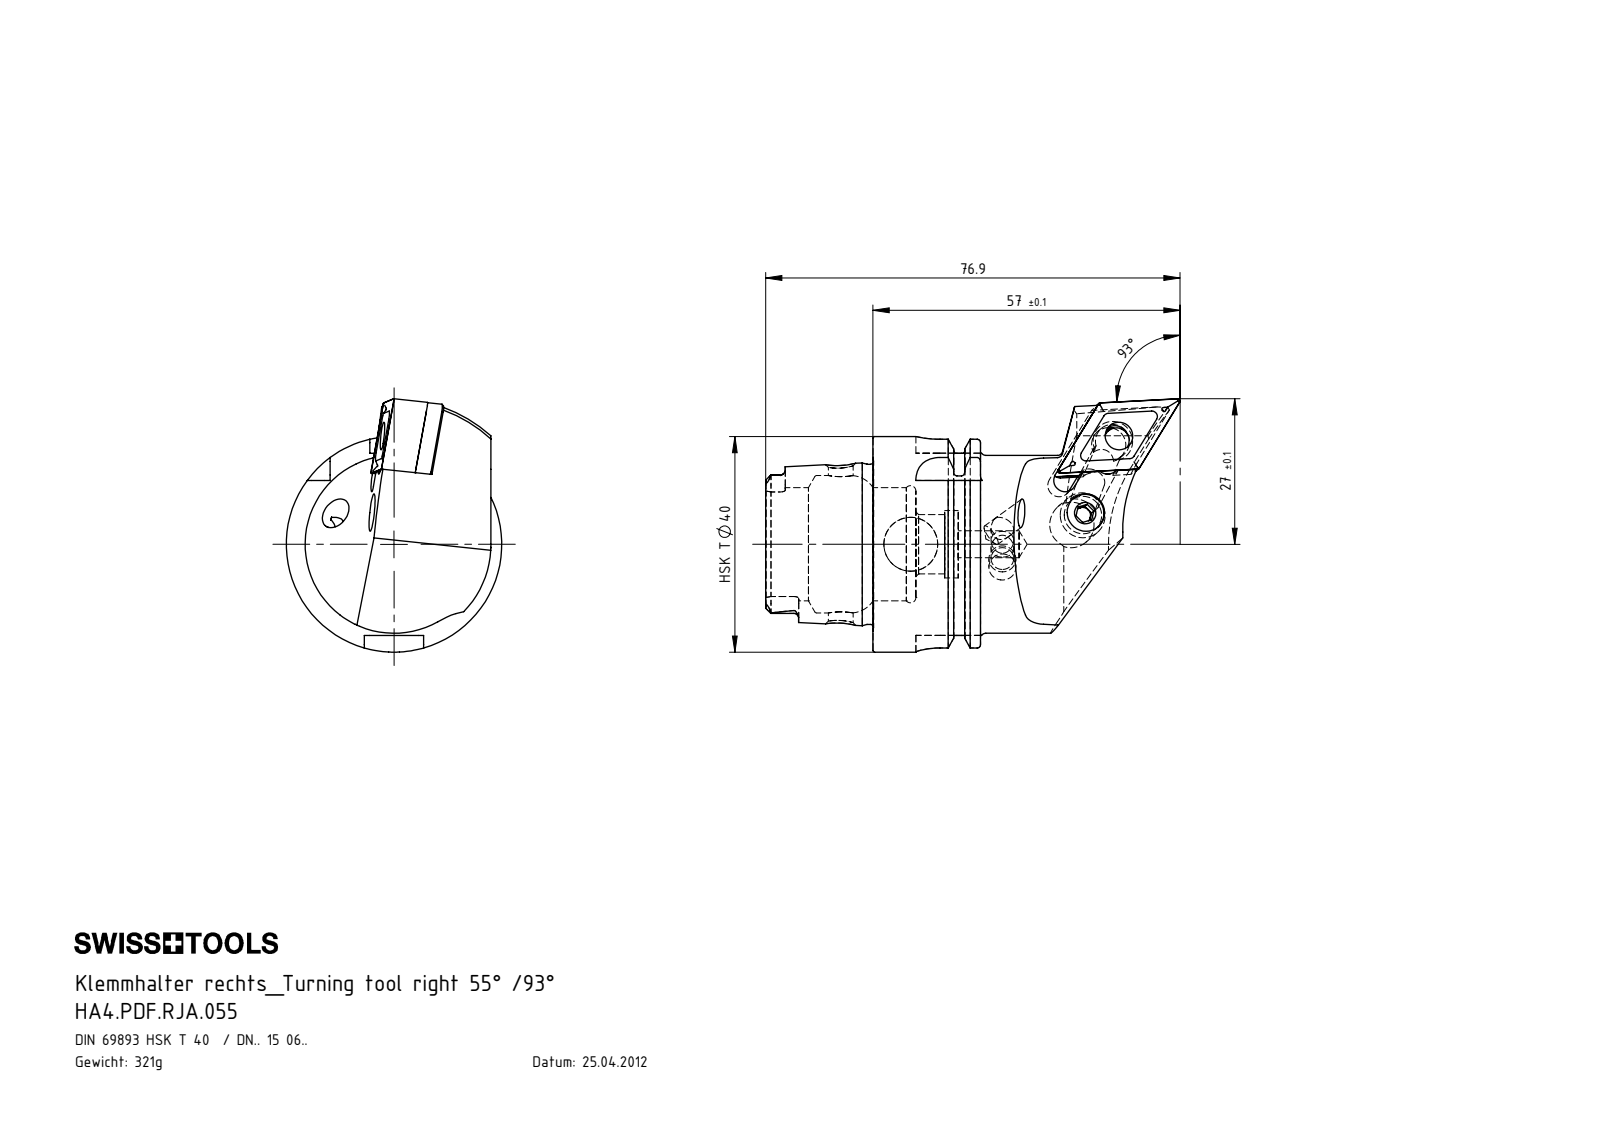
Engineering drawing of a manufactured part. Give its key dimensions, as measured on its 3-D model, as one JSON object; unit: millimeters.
{"part_name": "HA4-PDF.RJA.055; WDF-ER2.101.003_A; WDF-ER3.101.000_A; WCD-ER4.101.017_A (+4 more)", "step_written_by": "SolidWorks 2012 (CONFIG_CONTROL_DESIGN)", "units": "millimeters", "bodies": {"solids": 8, "faces": 385, "planar": 119, "cylindrical": 107, "other": 159}, "overall_size": [76.9, 47, 40], "volume_mm3": 42057, "surface_area_mm2": 16697, "round_holes": [[4.2, 2], [5, 2], [4, 1], [4.6, 1], [5.16, 1], [6.4, 1], [7, 1], [8.4, 1], [10, 1], [11, 1], [12.5, 1], [21, 1]], "round_bosses_or_shafts": [[40, 1], [34.75, 1], [33, 1], [29.71, 1], [8, 1], [7.9, 1], [6.4, 1], [5, 1]], "partial_cylinders_radius": [[0.9, 6], [0.4, 4], [1, 4], [4.5, 4], [1.82, 2], [1.88, 2], [2.5, 2], [2.1, 1]], "face_to_face_distances": [6.02, 9.2, 3.18, 7.95, 19.95, 12, 12.33, 19.9, 27.85, 39.85], "hole_center_spacings": [15.61]}
